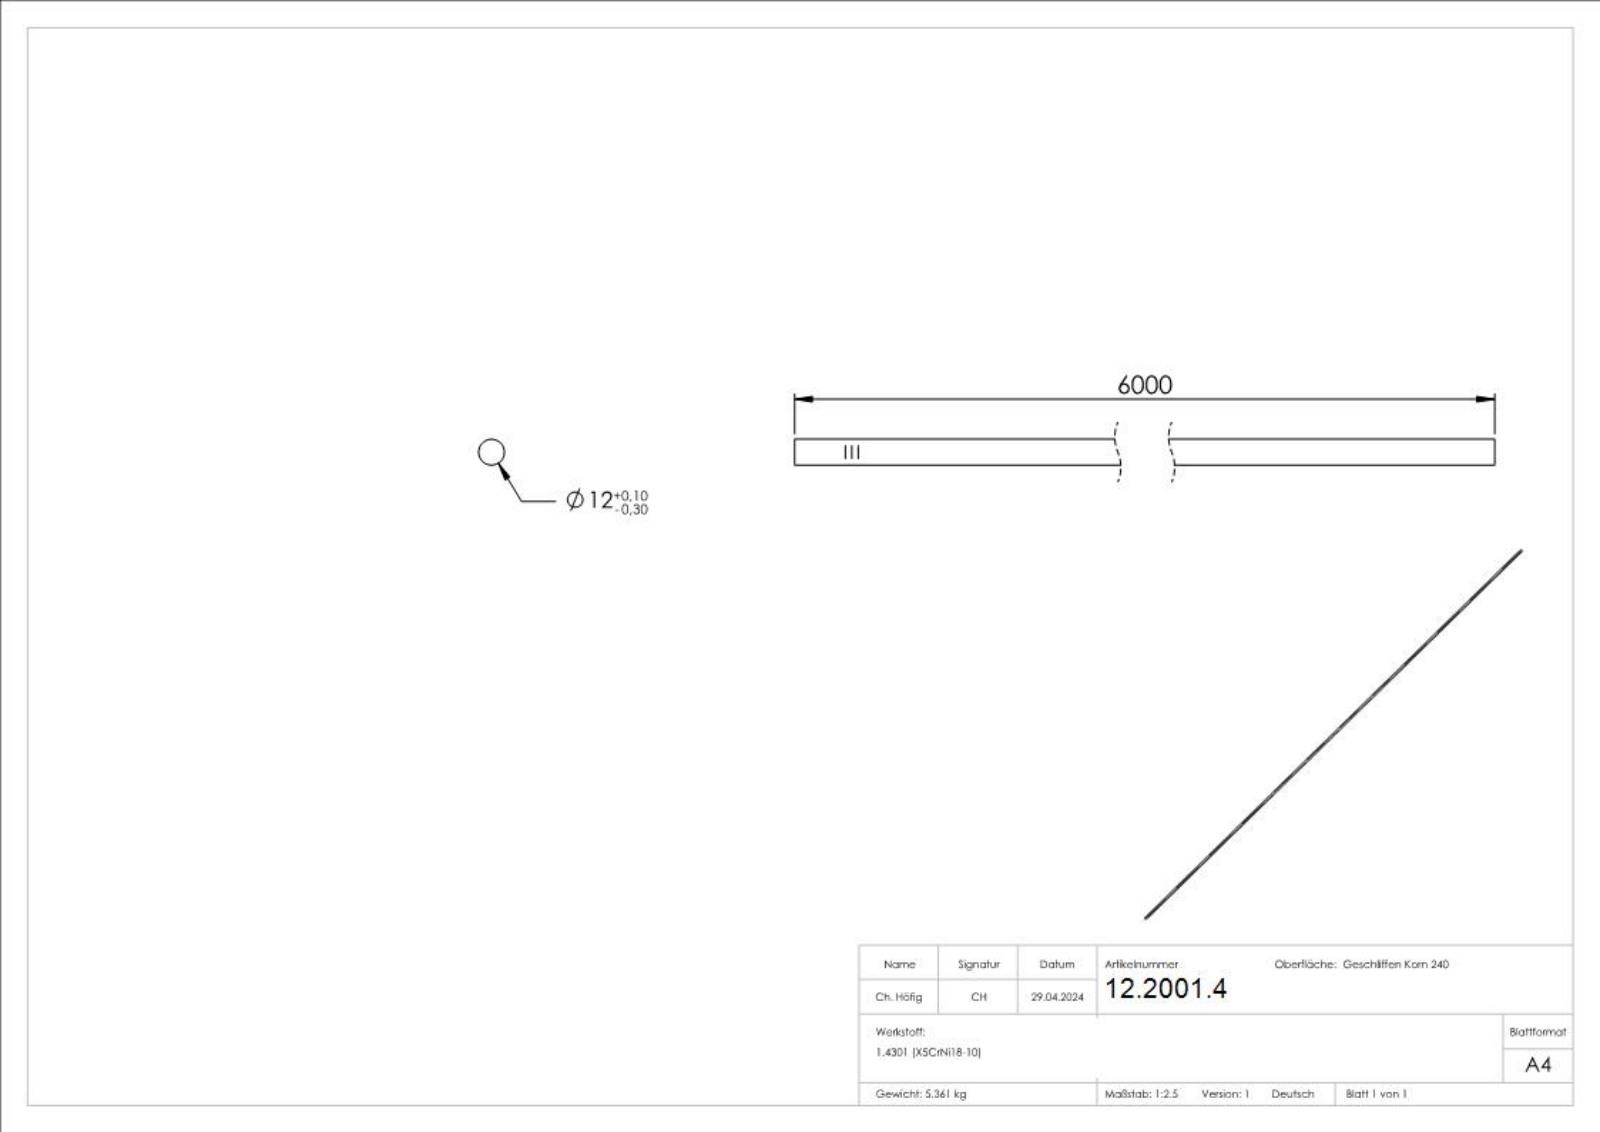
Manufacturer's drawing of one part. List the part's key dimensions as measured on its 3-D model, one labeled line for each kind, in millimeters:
Part name (STEP PRODUCT): 57101-240
STEP written by: SolidWorks 2018 (CONFIG_CONTROL_DESIGN)
Units: millimetres
Bodies: 1 solid, 258 faces (115 planar, 31 cylindrical, 112 other)
Overall size (bounding box): 6000 × 12 × 12
Volume: 678 584 mm³ · Surface area: 226 428 mm²
Round bosses / shafts (diameter × count): ⌀12 ×1
Partial cylindrical surfaces — rounded edges, fillets, slot ends (radius × count): R5.9 ×1
Main face-to-face distances: 6000, 0.76, 0.66, 0.79, 0.73, 1.13, 1.28, 3.17, 2999.84, 3000.16
